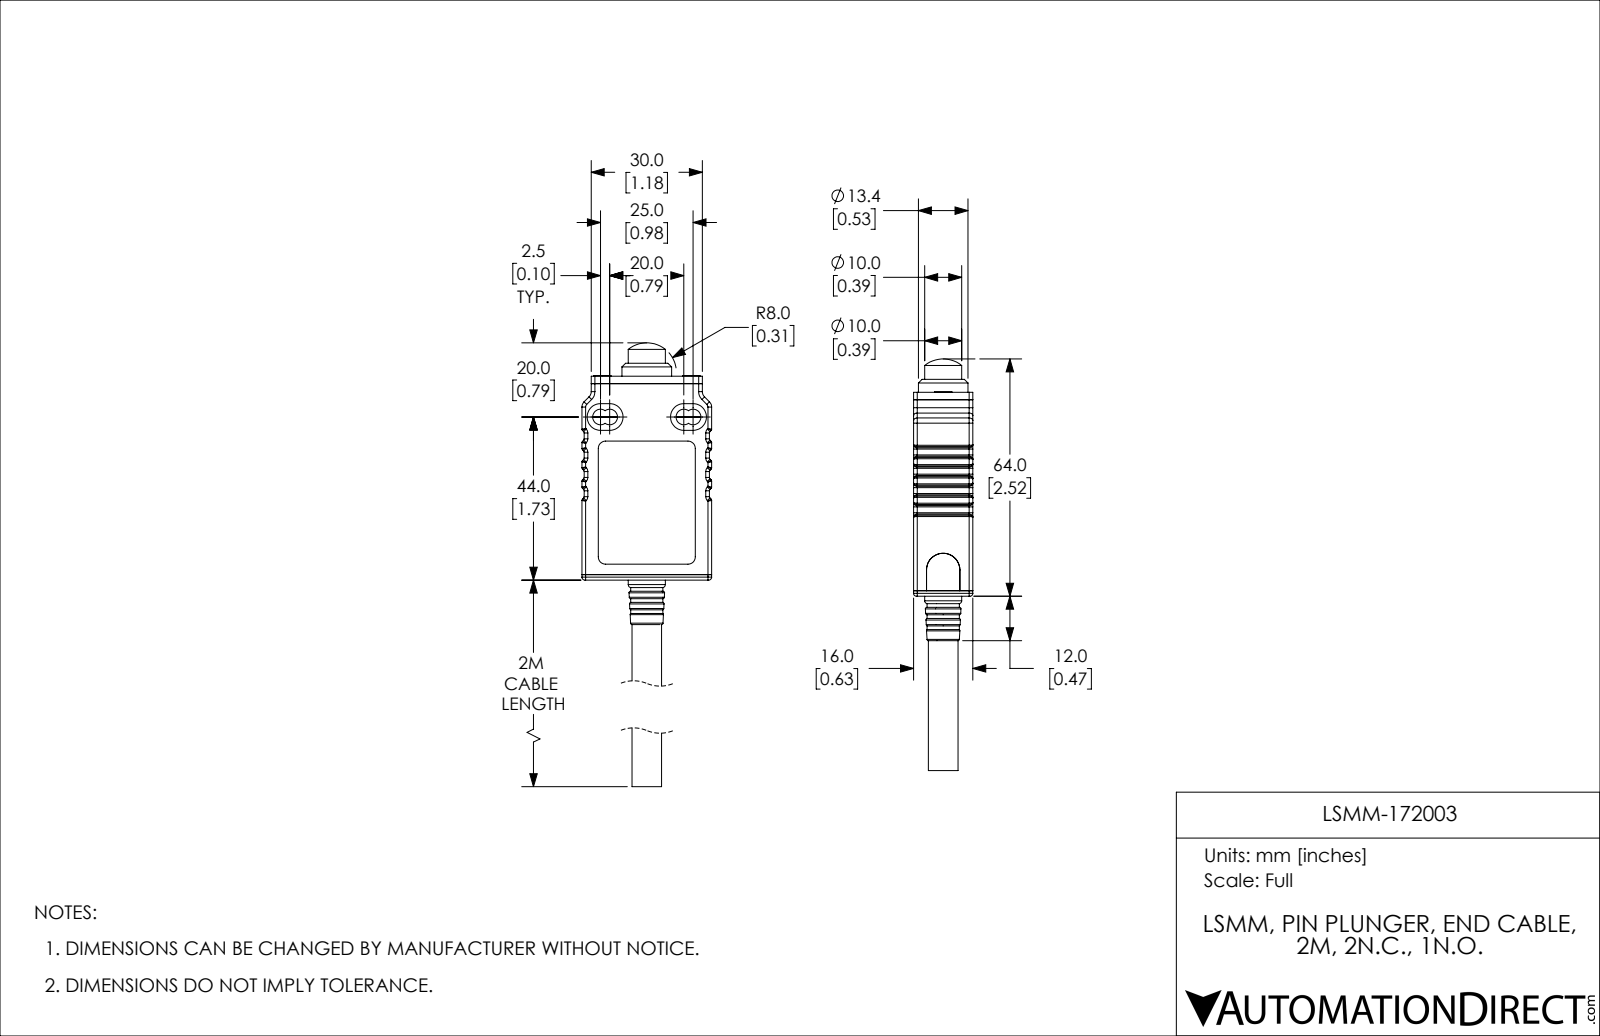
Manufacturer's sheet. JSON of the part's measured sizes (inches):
{"part_name": "170-LSPM-Pin Plunger (Cable End Exit) (STEP format)", "step_written_by": "SolidWorks 2015 (CONFIG_CONTROL_DESIGN)", "units": "inches", "bodies": {"solids": 10, "faces": 671, "planar": 230, "cylindrical": 289, "other": 152}, "overall_size": [4.37, 1.378, 0.63], "volume_in3": 1.055, "surface_area_in2": 27.83, "round_holes": [[0.079, 2], [0.098, 2], [0.102, 2], [0.157, 1], [0.213, 1], [0.315, 1], [0.354, 1], [0.398, 1], [0.441, 1], [0.531, 1], [0.575, 1]], "round_bosses_or_shafts": [[0.185, 2], [0.579, 1], [0.528, 1], [0.433, 1], [0.417, 1], [0.394, 1], [0.386, 1], [0.343, 1]], "partial_cylinders_radius": [[0.02, 74], [0.039, 52], [0.079, 8], [0.031, 4], [0.083, 4], [0.142, 4], [0.012, 3], [0.008, 2]], "face_to_face_distances": [0.059, 0.618, 0.047, 0.571, 0.559, 0.039, 0.079, 0.098, 0.606, 0.512], "hole_center_spacings": [0.472, 0.945]}
